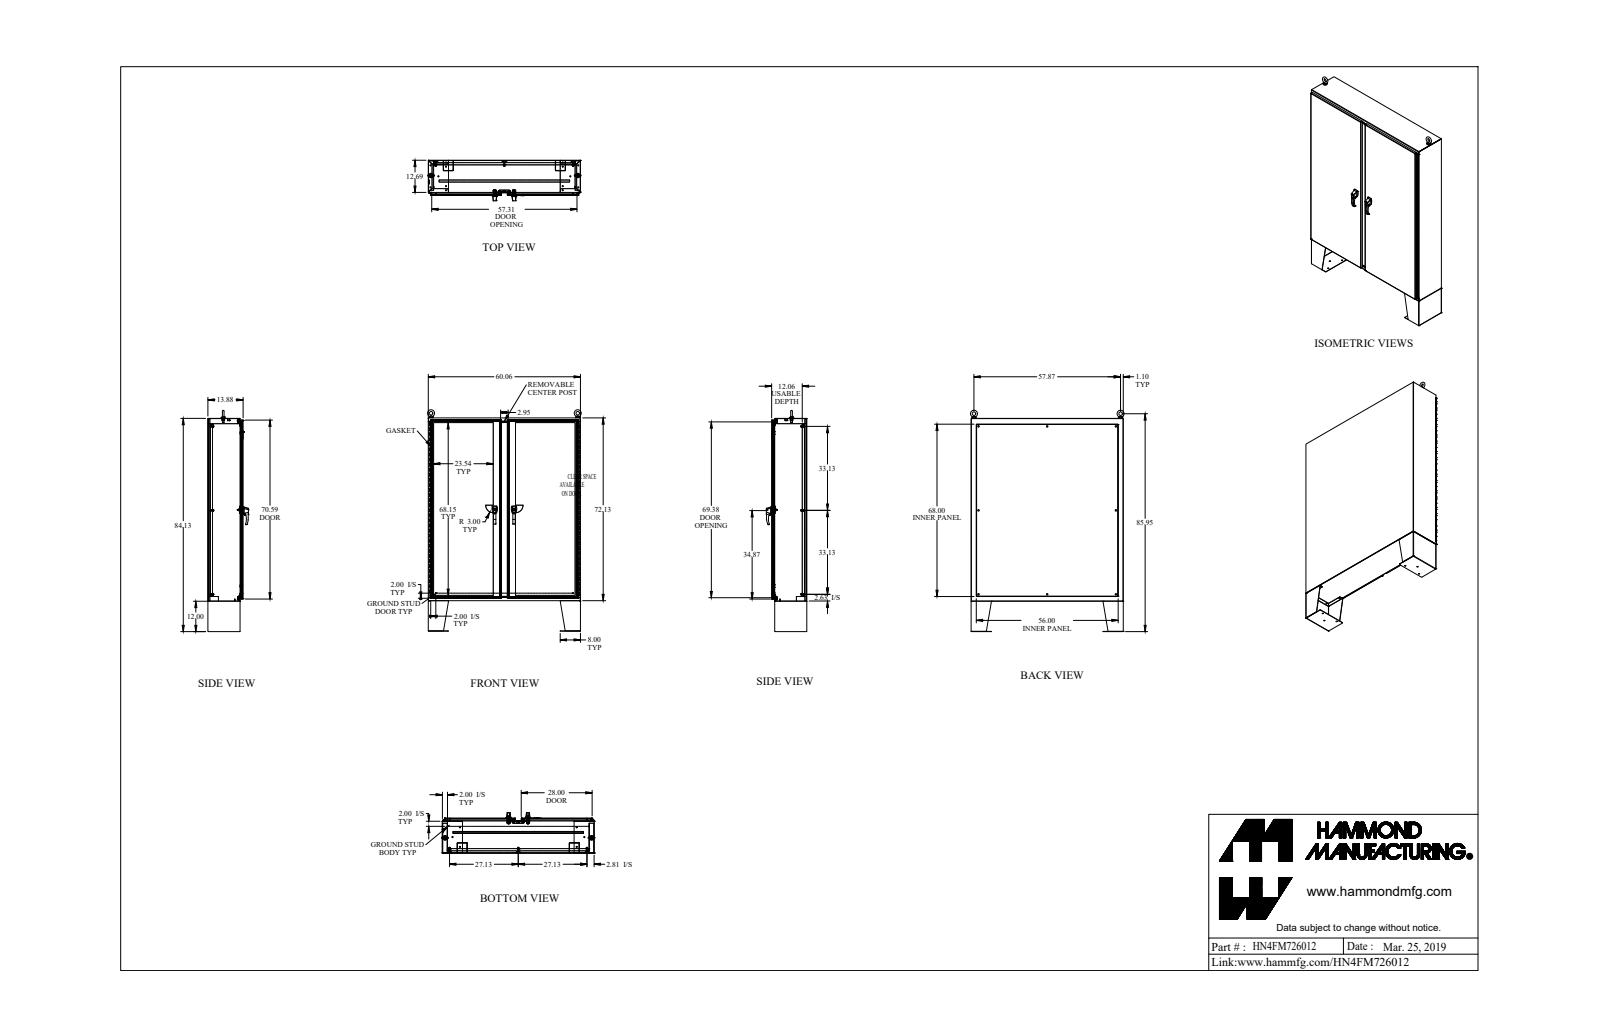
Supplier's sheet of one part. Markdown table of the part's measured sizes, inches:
| quantity | value |
| --- | --- |
| part name | HN4FM726012 |
| STEP written by | SolidWorks 2018 (AUTOMOTIVE_DESIGN) |
| units | inches |
| bodies | 132 solids, 3996 faces (1828 planar, 1795 cylindrical, 373 other) |
| overall size | 87.315 × 60.607 × 15.99 |
| volume | 2 162 in³ |
| surface area | 40 631 in² |
| round holes (diameter × count) | 0.304 × 24, 0.437 × 14, 0.307 × 8, 0.35 × 8, 0.563 × 8, 0.25 × 6, 0.445 × 6, 0.281 × 4, 0.313 × 4, 0.39 × 4, 0.201 × 3, 0.313 × 3 |
| round bosses / shafts (diameter × count) | 1 × 10, 0.65 × 8, 0.375 × 8, 0.33 × 8, 0.281 × 8, 0.75 × 4, 0.625 × 4, 0.44 × 4 |
| partial cylindrical surfaces (radius × count) | 0.5 × 33, 0.018 × 32, 0.125 × 32, 0.06 × 28, 0.048 × 27, 0.143 × 27, 0.03 × 12, 0.09 × 12 |
| main face-to-face distances | 0.125, 0.095, 1.687, 13.78, 13.655, 13.75, 13.875, 1.812, 11.968, 12.063 |
| hole center spacings | 6, 12, 18, 24, 30, 36, 42, 4.888 |
